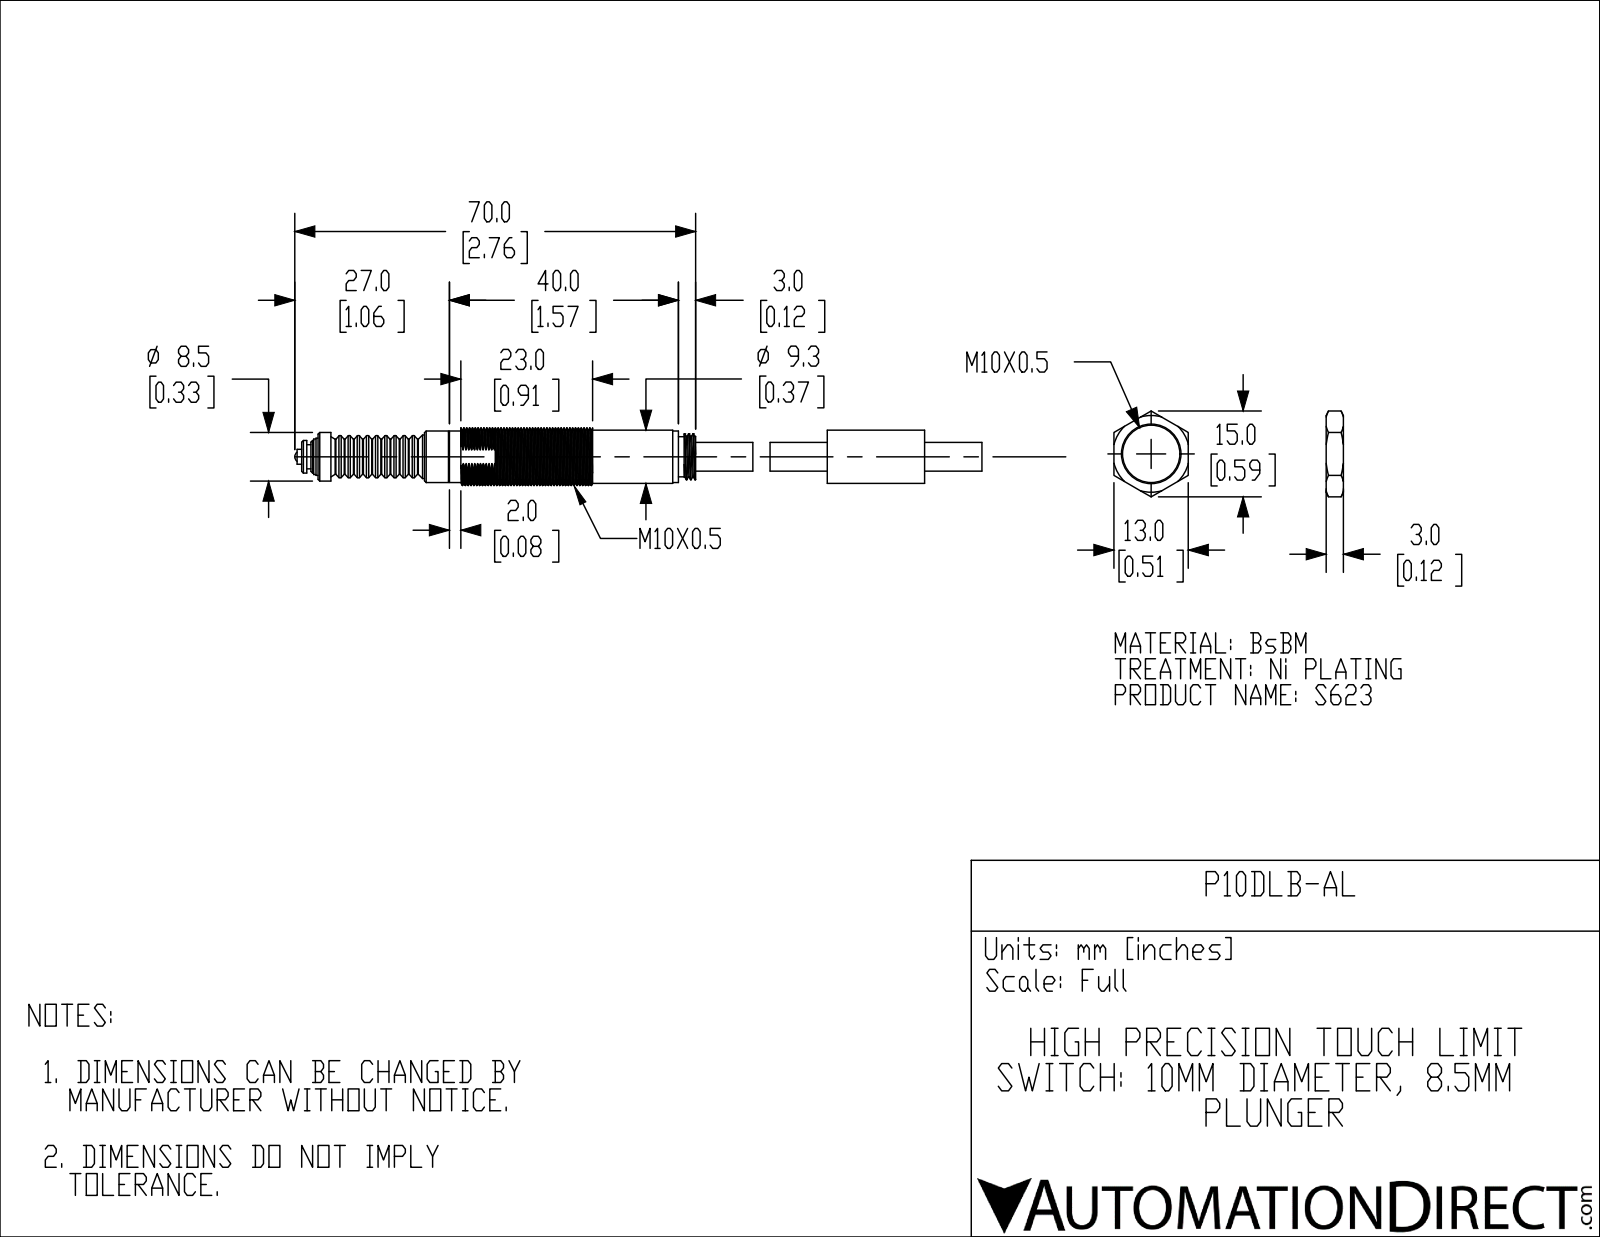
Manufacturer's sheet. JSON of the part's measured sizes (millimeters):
{"part_name": "P10DLB-AL", "step_written_by": "SolidWorks 2018 (AUTOMOTIVE_DESIGN)", "units": "millimeters", "bodies": {"solids": 2, "faces": 96, "planar": 27, "cylindrical": 20, "other": 49}, "overall_size": [120, 10, 10], "volume_mm3": 5880, "surface_area_mm2": 3308, "round_bosses_or_shafts": [[10, 1], [9.3, 1], [9, 1], [8.5, 1], [8, 1], [7.6, 1], [7, 1], [6.5, 1]], "face_to_face_distances": [13, 10, 17, 40, 3, 27, 43, 23, 53, 9]}
